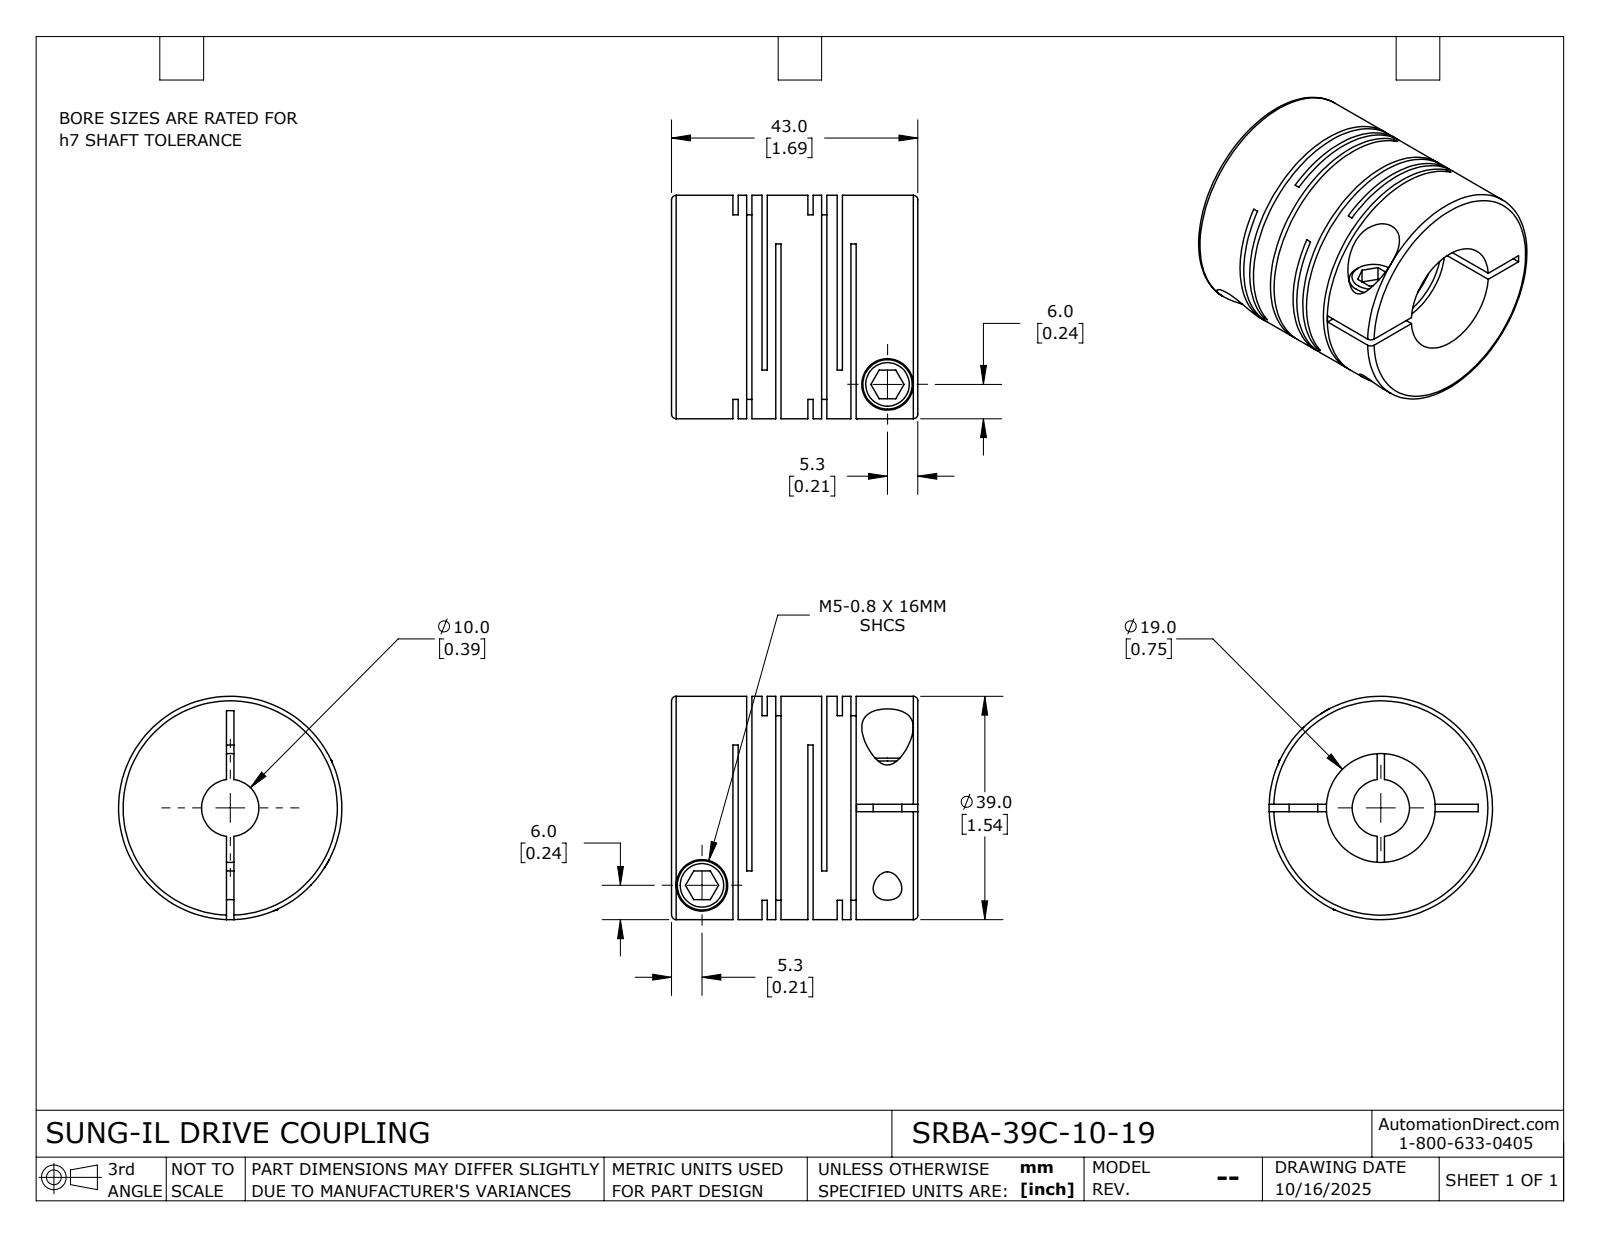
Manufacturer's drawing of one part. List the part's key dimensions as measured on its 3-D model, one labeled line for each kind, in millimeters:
Part name (STEP PRODUCT): SRBA-39C-10-19
STEP written by: SolidWorks 2024 (CONFIG_CONTROL_DESIGN)
Units: millimetres
Bodies: 1 solid, 115 faces (60 planar, 42 cylindrical, 13 other)
Overall size (bounding box): 43 × 39 × 39
Volume: 34 575 mm³ · Surface area: 21 954 mm²
Round holes (diameter × count): ⌀5 ×2, ⌀9 ×2, ⌀10 ×1, ⌀19 ×1
Round bosses / shafts (diameter × count): ⌀8.6 ×2, ⌀39 ×1
Main face-to-face distances: 13.1, 0.92, 2.4, 5.1, 10.7, 14.02, 18.2, 12.18, 3.32, 7.5
